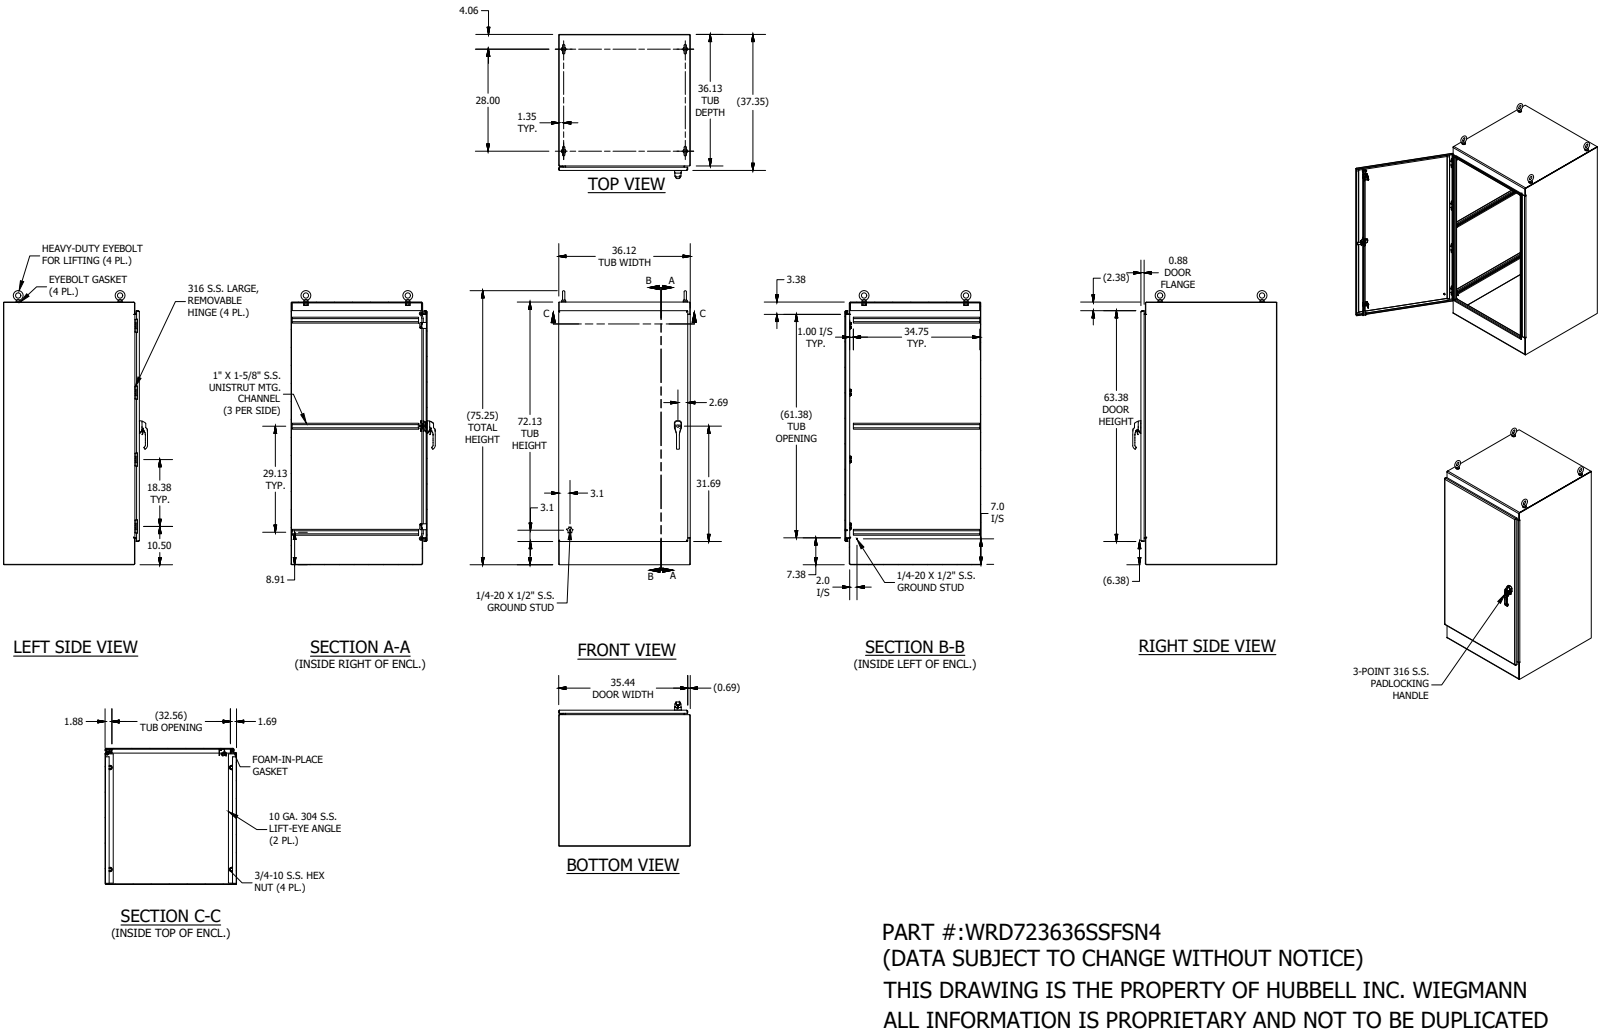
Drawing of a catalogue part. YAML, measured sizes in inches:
part_name: "WRD723636SSFSN4"
step_written_by: "SolidWorks 2019 (AUTOMOTIVE_DESIGN)"
units: inches
bodies: {solids: 111, faces: 4033, planar: 1612, cylindrical: 1390, other: 1031}
overall_size: [75.248, 39.598, 36.129]
volume: 1630
surface_area: 30556
round_holes:
  - {diameter: 0.14, count: 24}
  - {diameter: 0.195, count: 8}
  - {diameter: 0.262, count: 8}
  - {diameter: 0.266, count: 8}
  - {diameter: 0.294, count: 8}
  - {diameter: 0.65, count: 8}
  - {diameter: 0.136, count: 4}
  - {diameter: 0.164, count: 4}
  - {diameter: 0.187, count: 4}
  - {diameter: 0.201, count: 4}
  - {diameter: 0.642, count: 4}
  - {diameter: 0.813, count: 4}
round_bosses_or_shafts:
  - {diameter: 0.625, count: 8}
  - {diameter: 0.25, count: 7}
  - {diameter: 1.25, count: 4}
  - {diameter: 1.12, count: 4}
  - {diameter: 0.75, count: 4}
  - {diameter: 0.237, count: 4}
  - {diameter: 0.236, count: 3}
  - {diameter: 1, count: 2}
partial_cylinders:
  - {radius: 0.02, count: 172}
  - {radius: 0.012, count: 114}
  - {radius: 0.125, count: 34}
  - {radius: 0.019, count: 21}
  - {radius: 0.062, count: 18}
  - {radius: 0.05, count: 14}
  - {radius: 0.063, count: 14}
  - {radius: 0.079, count: 14}
face_to_face_distances: [0.104, 36.021, 35.917, 36.125, 72.021, 37.245, 37.141, 37.349, 37.245, 0.104]
hole_center_spacings: [0.018, 0.023, 0.029, 0.38, 0.76, 1, 18.375, 36.75]
